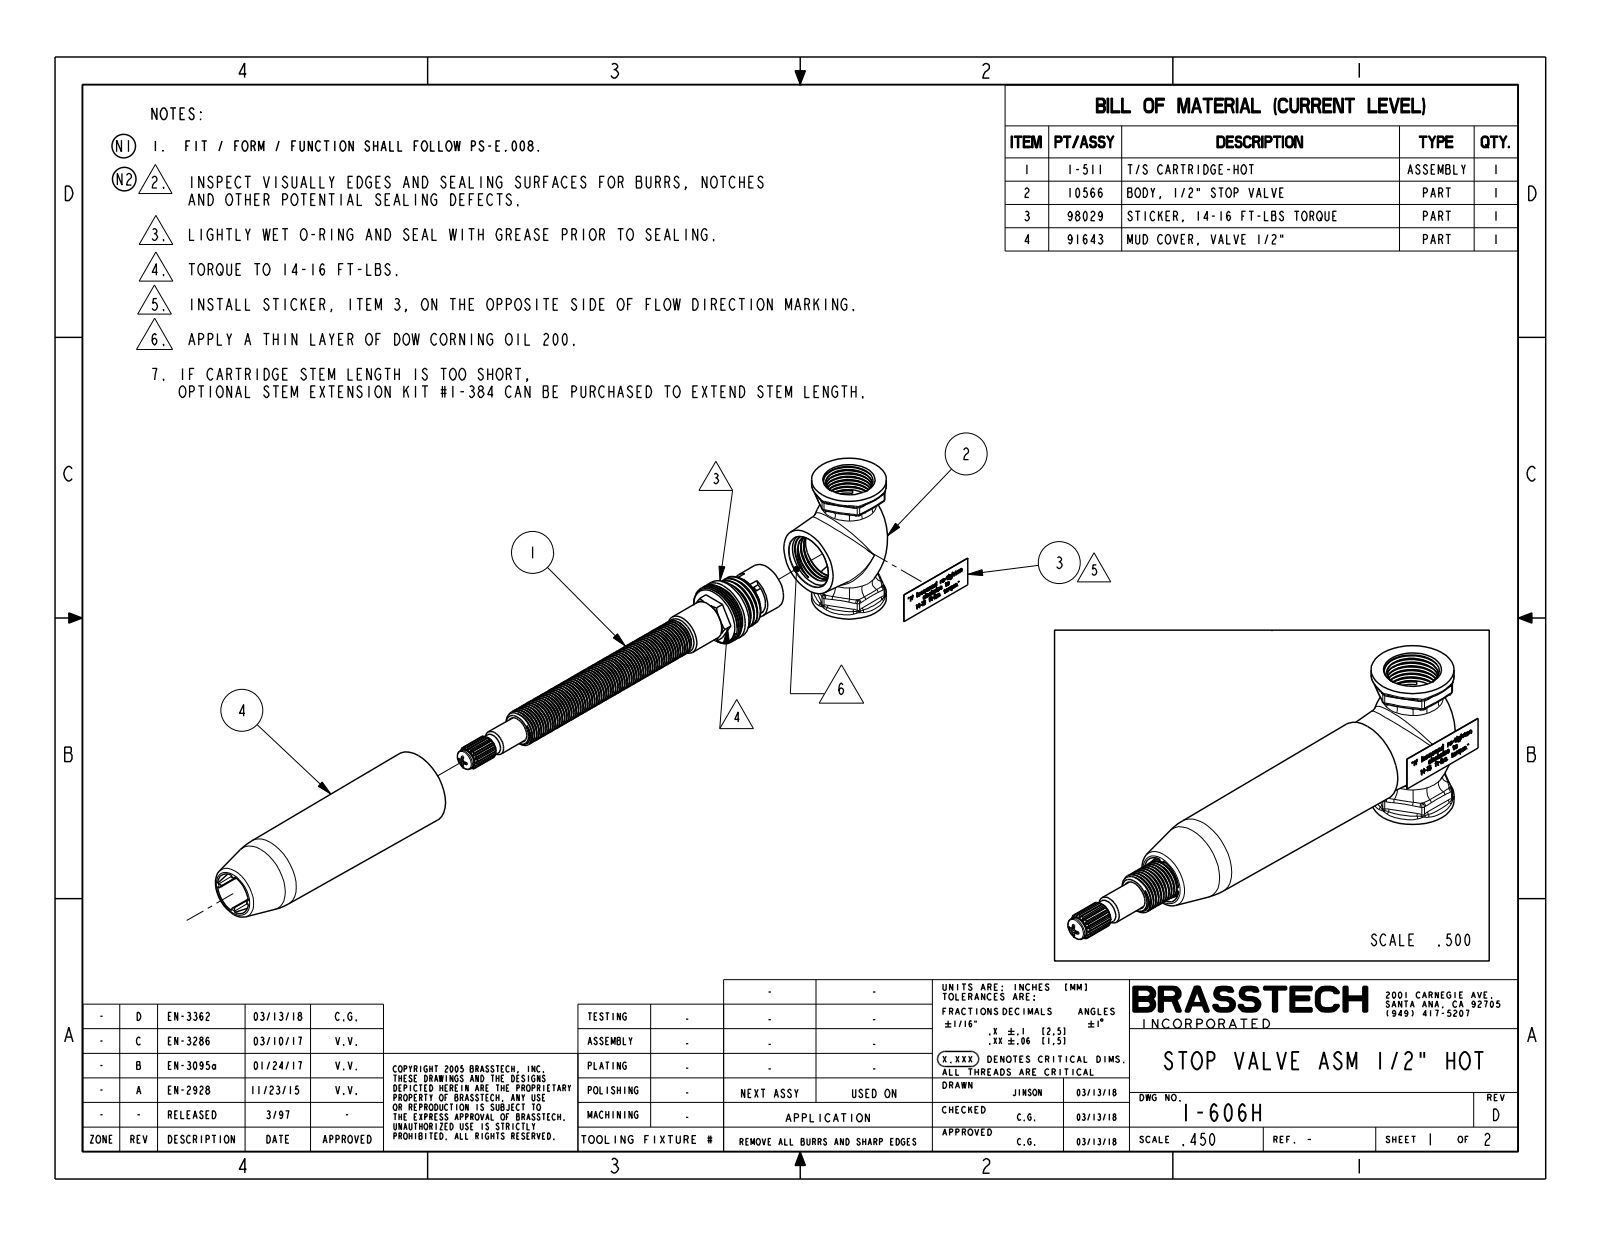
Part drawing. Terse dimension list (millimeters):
name: 1-148; 10489; 12062; 92850 (+3 more)
written by: PRO/ENGINEER BY PARAMETRIC TECHNOLOGY CORPORATION, 2013150 (CONFIG_CONTROL_DESIGN)
unit: mm
bodies: 5 solids, 2011 faces (591 planar, 941 cylindrical, 479 other)
size: 183.7 × 56 × 29.9
volume: 38 000 mm³; area: 36 320 mm²
holes: 1× ⌀3.3, 1× ⌀4.2, 1× ⌀4.4, 1× ⌀8.4, 1× ⌀9, 1× ⌀10.3, 1× ⌀11.2, 1× ⌀13.1, 1× ⌀14.5, 1× ⌀16.1, 1× ⌀17.4, 1× ⌀18
bosses: 2× ⌀0.7, 1× ⌀29, 1× ⌀24, 1× ⌀21.1, 1× ⌀20.9, 1× ⌀18.5, 1× ⌀15.9, 1× ⌀15.7
rounds: 38× R1, 5× R1, 4× R2, 1× R3.5, 1× R3.8, 1× R4.2, 1× R4.7, 1× R6.6
face distances: 4.7, 4.7, 56, 22.2, 1.3, 23.5, 2, 2.7, 25.1, 4.7
